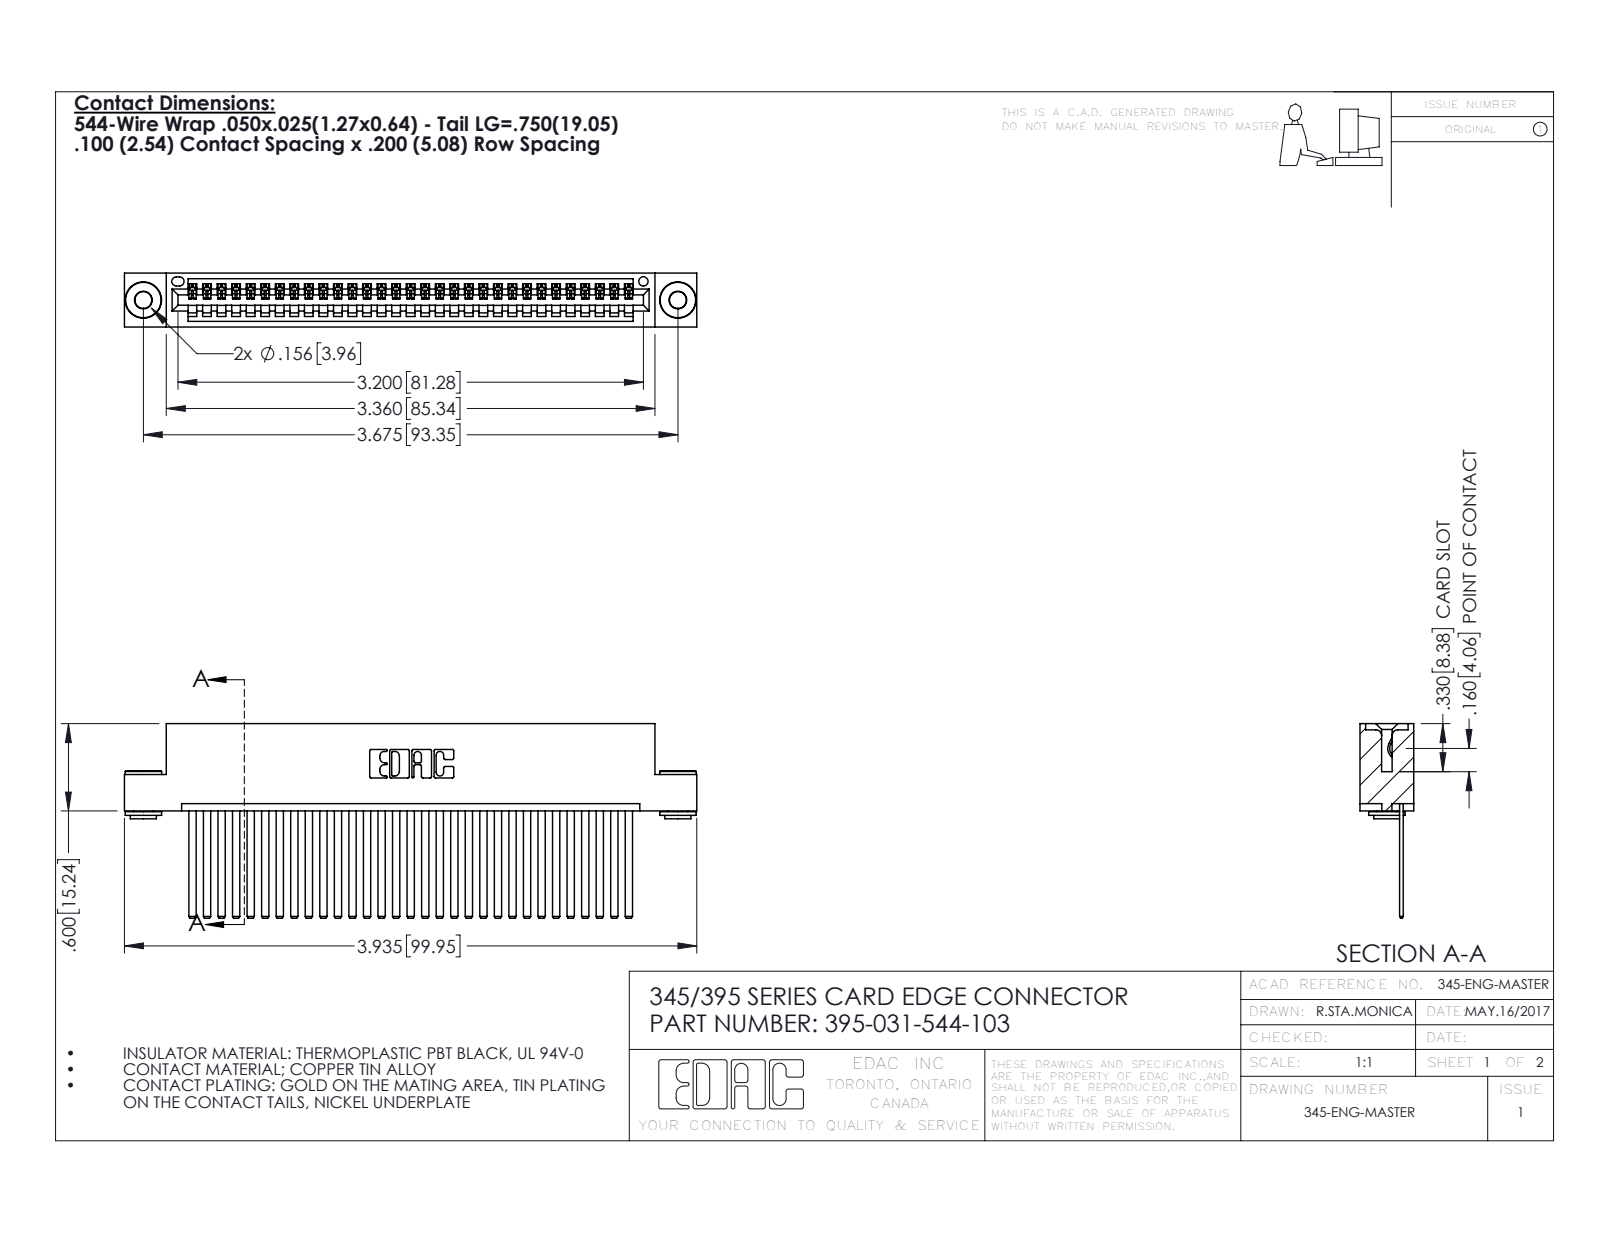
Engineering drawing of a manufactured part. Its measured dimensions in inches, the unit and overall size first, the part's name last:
Units: inches
Overall size (bounding box): 3.935 × 1.337 × 0.37
Round holes (diameter × count): ⌀0.116 ×2, ⌀0.156 ×2, ⌀0.064 ×1
Round bosses / shafts (diameter × count): ⌀0.25 ×2, ⌀0.18 ×2, ⌀0.136 ×2
Partial cylindrical surfaces — rounded edges, fillets, slot ends (radius × count): R0.006 ×62, R0.01 ×22, R0.007 ×6, R0.031 ×6, R0.026 ×3, R0.031 ×2, R0.04 ×2, R0.014 ×1
Main face-to-face distances: 0.072, 0.298, 0.025, 0.098, 0.272, 0.2, 0.37, 0.225, 0.149, 0.072
Hole centre spacings: 0.27, 3.44, 3.675
Volume: 0.597 in³ · Surface area: 21.92 in²
Bodies: 34 solids, 1776 faces (1206 planar, 562 cylindrical, 8 other)
Part name (STEP PRODUCT): 345-250-002_345-250-002-102; 345-292-001_345-293-144; 395-031-544-103; 345 Part_Flush Mounting Lugs - 0.156 Dia-TH
STEP written by: SolidWorks 2016 (CONFIG_CONTROL_DESIGN)
